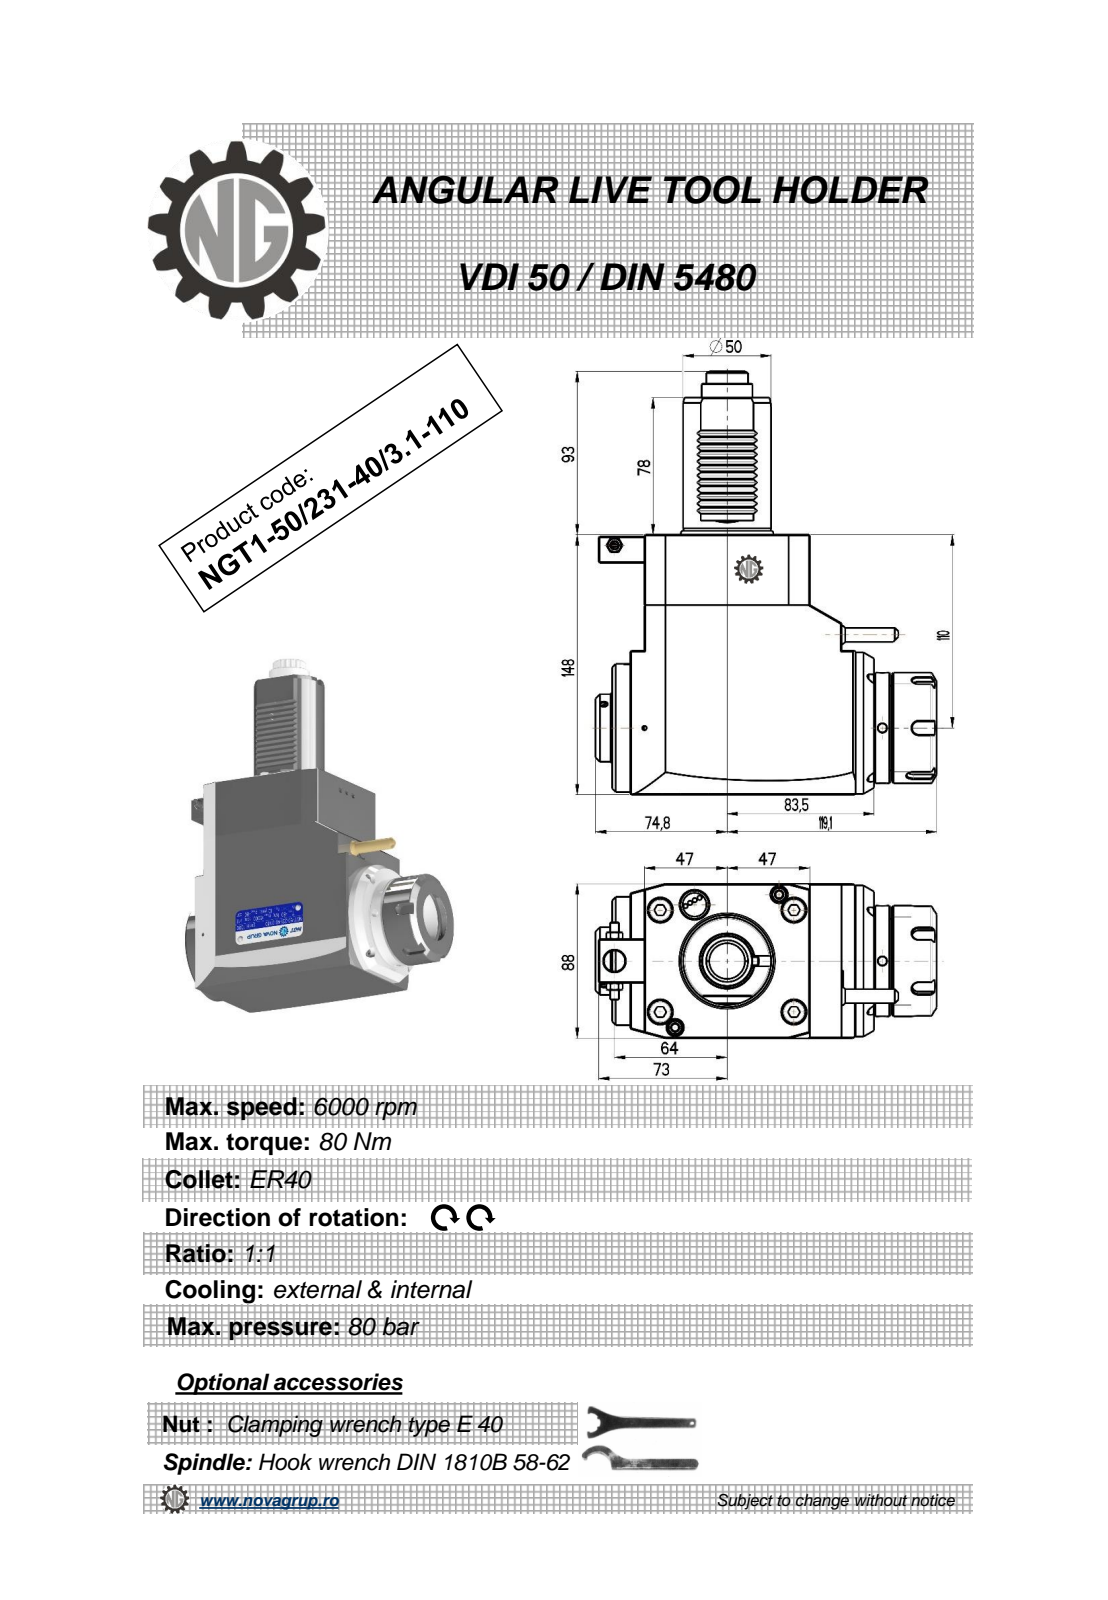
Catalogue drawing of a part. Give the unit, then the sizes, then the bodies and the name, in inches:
Units: inches
Overall size (bounding box): 9.488 × 7.634 × 3.465
Round holes (diameter × count): ⌀0.197 ×3, ⌀0.118 ×1, ⌀0.165 ×1, ⌀0.374 ×1, ⌀0.472 ×1, ⌀1.319 ×1
Round bosses / shafts (diameter × count): ⌀3.386 ×1, ⌀2.874 ×1, ⌀2.48 ×1, ⌀2.008 ×1, ⌀1.969 ×1, ⌀1.575 ×1, ⌀1.516 ×1, ⌀1.134 ×1
Partial cylindrical surfaces — rounded edges, fillets, slot ends (radius × count): R0.12 ×36, R0.01 ×12, R0.012 ×12, R0.008 ×6, R0.148 ×5, R0.416 ×1, R0.468 ×1, R0.689 ×1
Main face-to-face distances: 3.465, 5.827, 3.701, 0.315, 4.724, 1.437, 5.138, 0.72, 4.421, 5.858
Hole centre spacings: 2.065, 2.23, 3.996, 5.994, 7.259
Volume: 113.3 in³ · Surface area: 179.5 in²
Bodies: 1 solid, 525 faces (207 planar, 165 cylindrical, 153 other)
Part name (STEP PRODUCT): NGT1_50_231_40_3_1_110
STEP written by: PRO/ENGINEER BY PARAMETRIC TECHNOLOGY CORPORATION, 2010280 (CONFIG_CONTROL_DESIGN)
